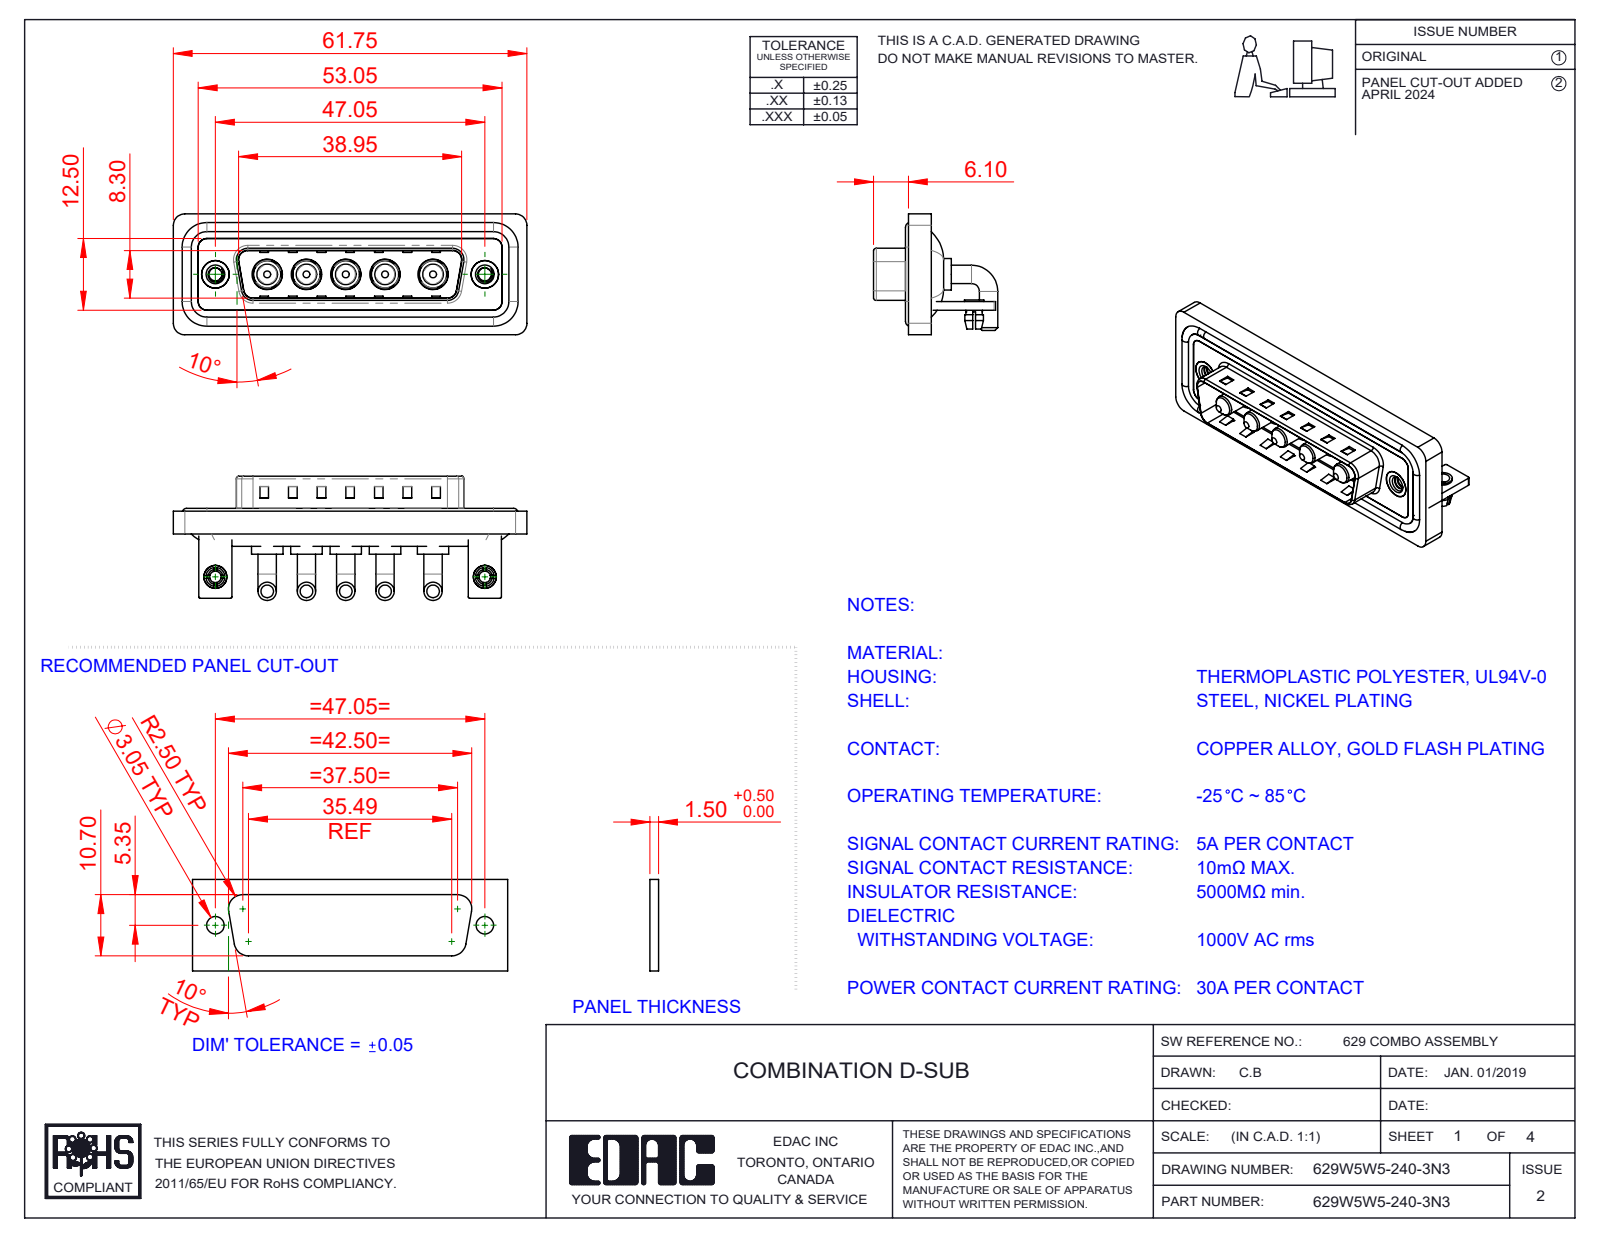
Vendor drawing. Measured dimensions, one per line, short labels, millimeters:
name: Power Pin_30A RA; 629Combo Shell Rear_25 Contacts; 629Combo Threaded Rivet_3; 629Combo Stabilizer Bracket (+5 more)
written by: SolidWorks 2023 (CONFIG_CONTROL_DESIGN)
unit: mm
bodies: 21 solids, 830 faces (327 planar, 343 cylindrical, 160 other)
size: 61.75 × 21.7 × 21.1
volume: 8 256 mm³; area: 13 161 mm²
holes: 5× ⌀4.85, 5× ⌀5.3, 2× ⌀2, 2× ⌀2.26, 2× ⌀2.5, 2× ⌀3.2, 2× ⌀4, 2× ⌀4.8, 2× ⌀5
bosses: 10× ⌀3.2, 5× ⌀5.5, 5× ⌀5.2, 5× ⌀4.75, 5× ⌀3.75, 5× ⌀3.6, 4× ⌀1.6, 2× ⌀4.9
rounds: 19× R2, 18× R1.5, 16× R0.25, 9× R0.5, 8× R1.6, 5× R2.1, 4× R0.6, 4× R0.65
face distances: 0.4, 1.5, 2.9, 0.8, 2.1, 1.1, 3.7, 4.5, 4.1, 1.2
hole spacings: 6.86, 13.73, 47.05, 6.85, 6.87, 8.37, 8.38, 9.04
